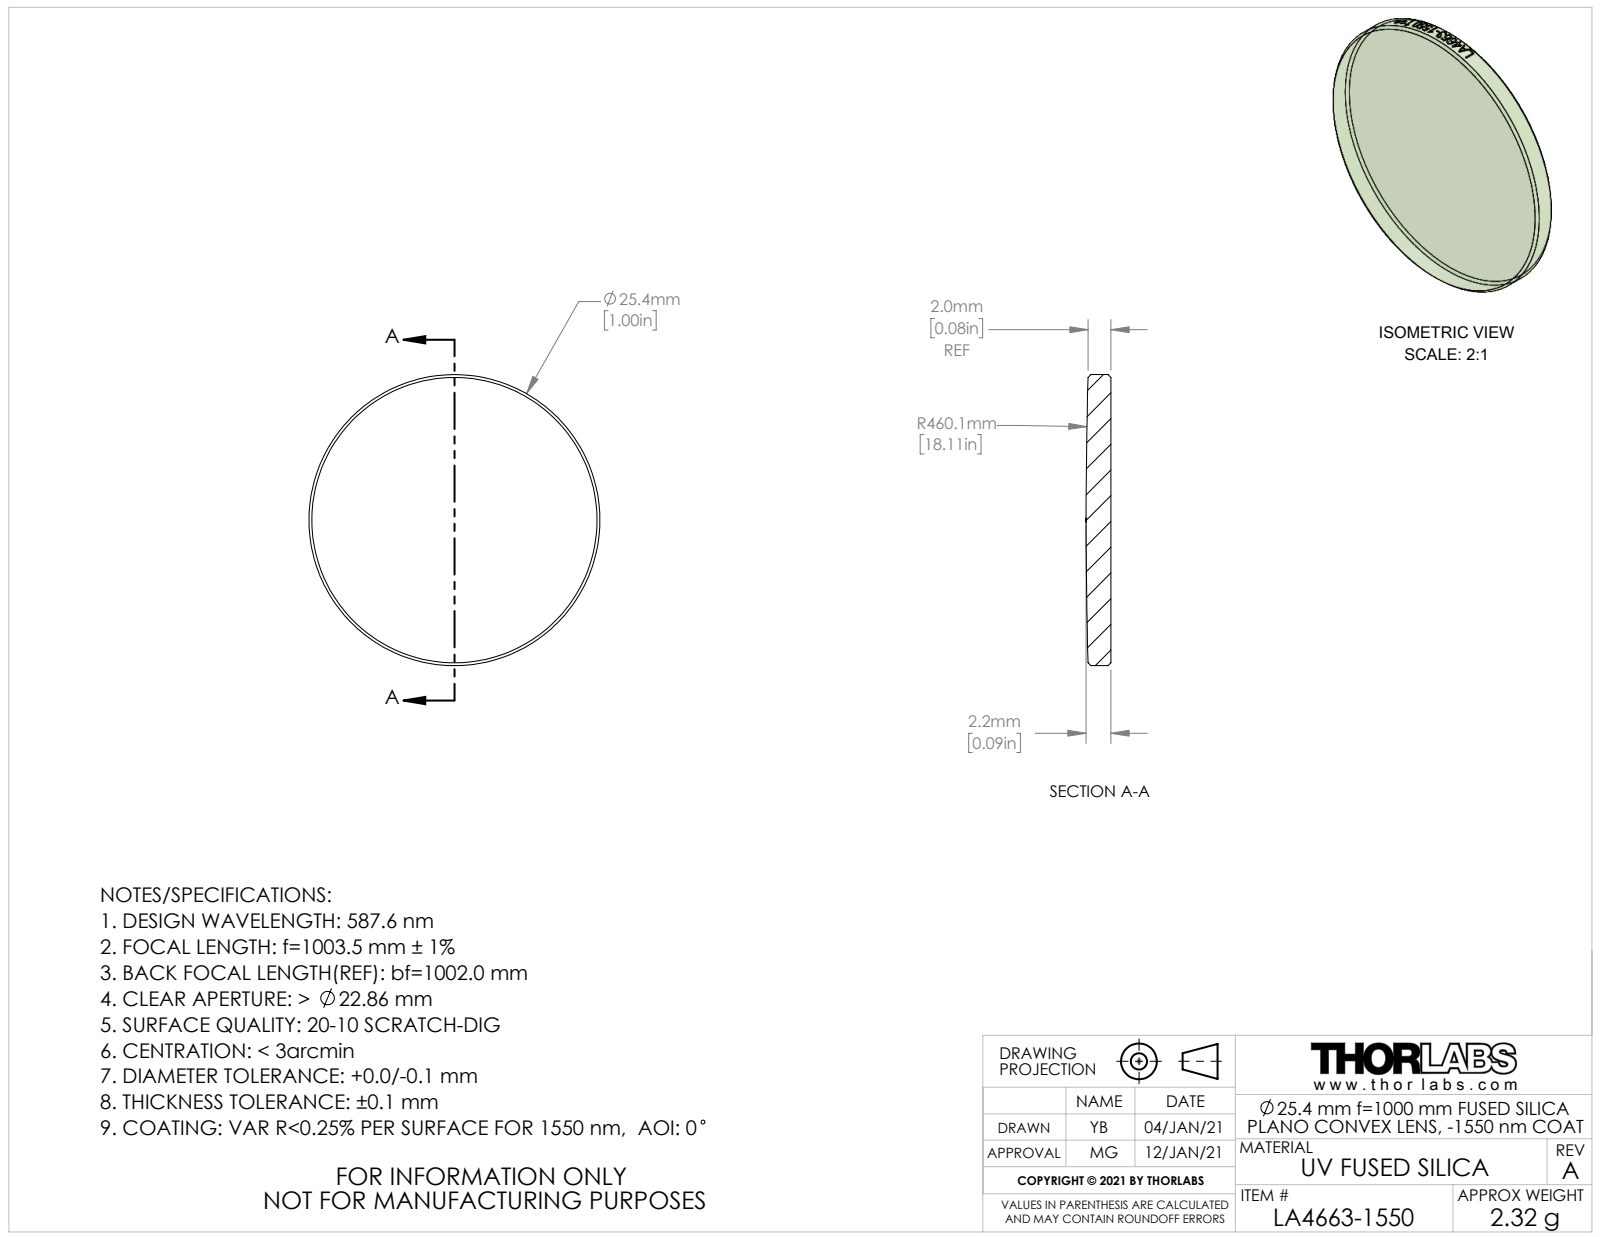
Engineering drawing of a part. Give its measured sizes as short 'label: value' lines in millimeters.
name: CTN015945-E0W
written by: SolidWorks 2018 (AUTOMOTIVE_DESIGN)
unit: mm
bodies: 1 solid, 32 faces (1 planar, 25 cylindrical, 6 other)
size: 25.4 × 25.4 × 2.2
volume: 1 000 mm³; area: 1 150 mm²
bosses: 1× ⌀25.4
